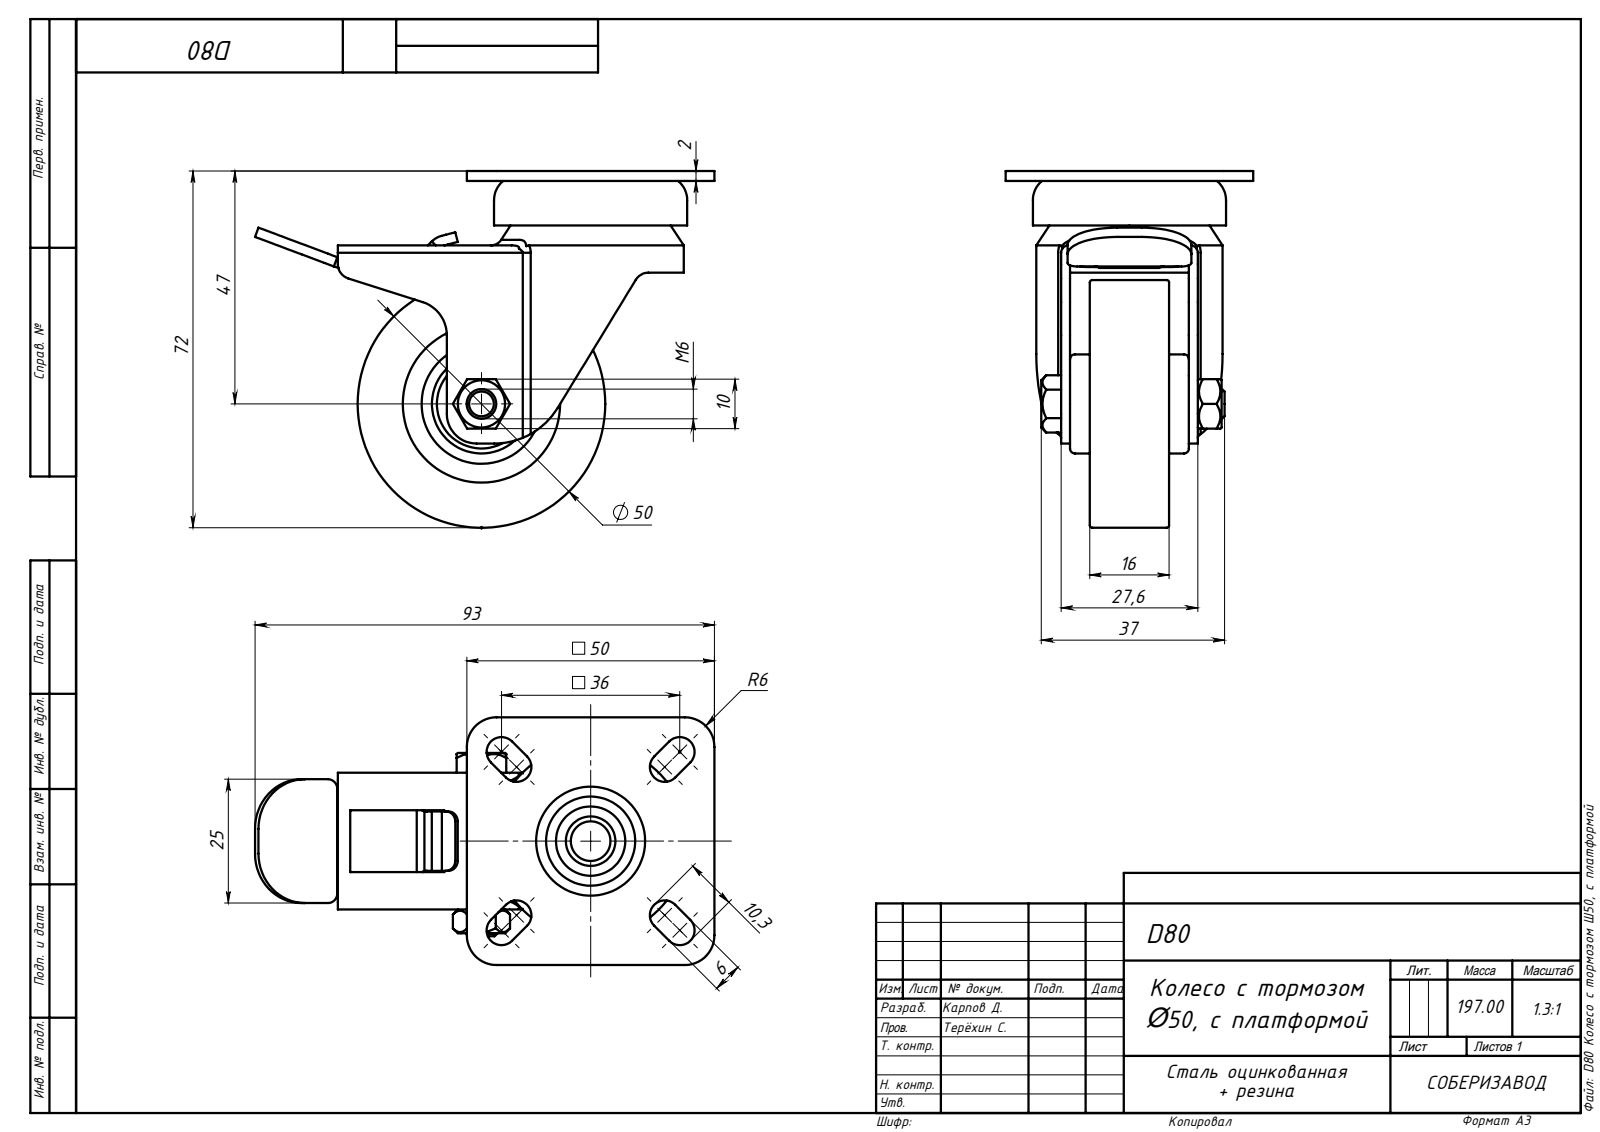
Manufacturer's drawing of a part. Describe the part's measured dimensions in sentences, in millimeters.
The part is named "D80 Болт_00; D80 Опора_00; D80 Гайка_00; D80 Колесо с тормозом O50, с платформой (+3 more)". Its 3-D file was written by "SolidWorks 2021 (AUTOMOTIVE_DESIGN)". It is 6 solids with 347 faces: 202 planar, 88 cylindrical and 57 other. Overall it measures 92.77 by 72 by 50 millimeters. Its volume is 50 831 cubic millimeters and its surface area 31 191 square millimeters. Round holes: 1 of diameter 5, 1 of diameter 6.2, 1 of diameter 12.5, 1 of diameter 18, 1 of diameter 37. Round bosses or shafts: 1 of diameter 50, 1 of diameter 39, 1 of diameter 29, 1 of diameter 25, 1 of diameter 20, 1 of diameter 10, 1 of diameter 6. Partial cylindrical surfaces (rounded edges, fillets, slot ends): 12 of radius 2, 10 of radius 3, 5 of radius 2.5, 5 of radius 6, 4 of radius 1, 4 of radius 1.5, 3 of radius 4.5, 2 of radius 10. The main face-to-face distances are 4, 2, 1.8, 15, 5.8, 16, 20, 25.8, 21.8, 13.
